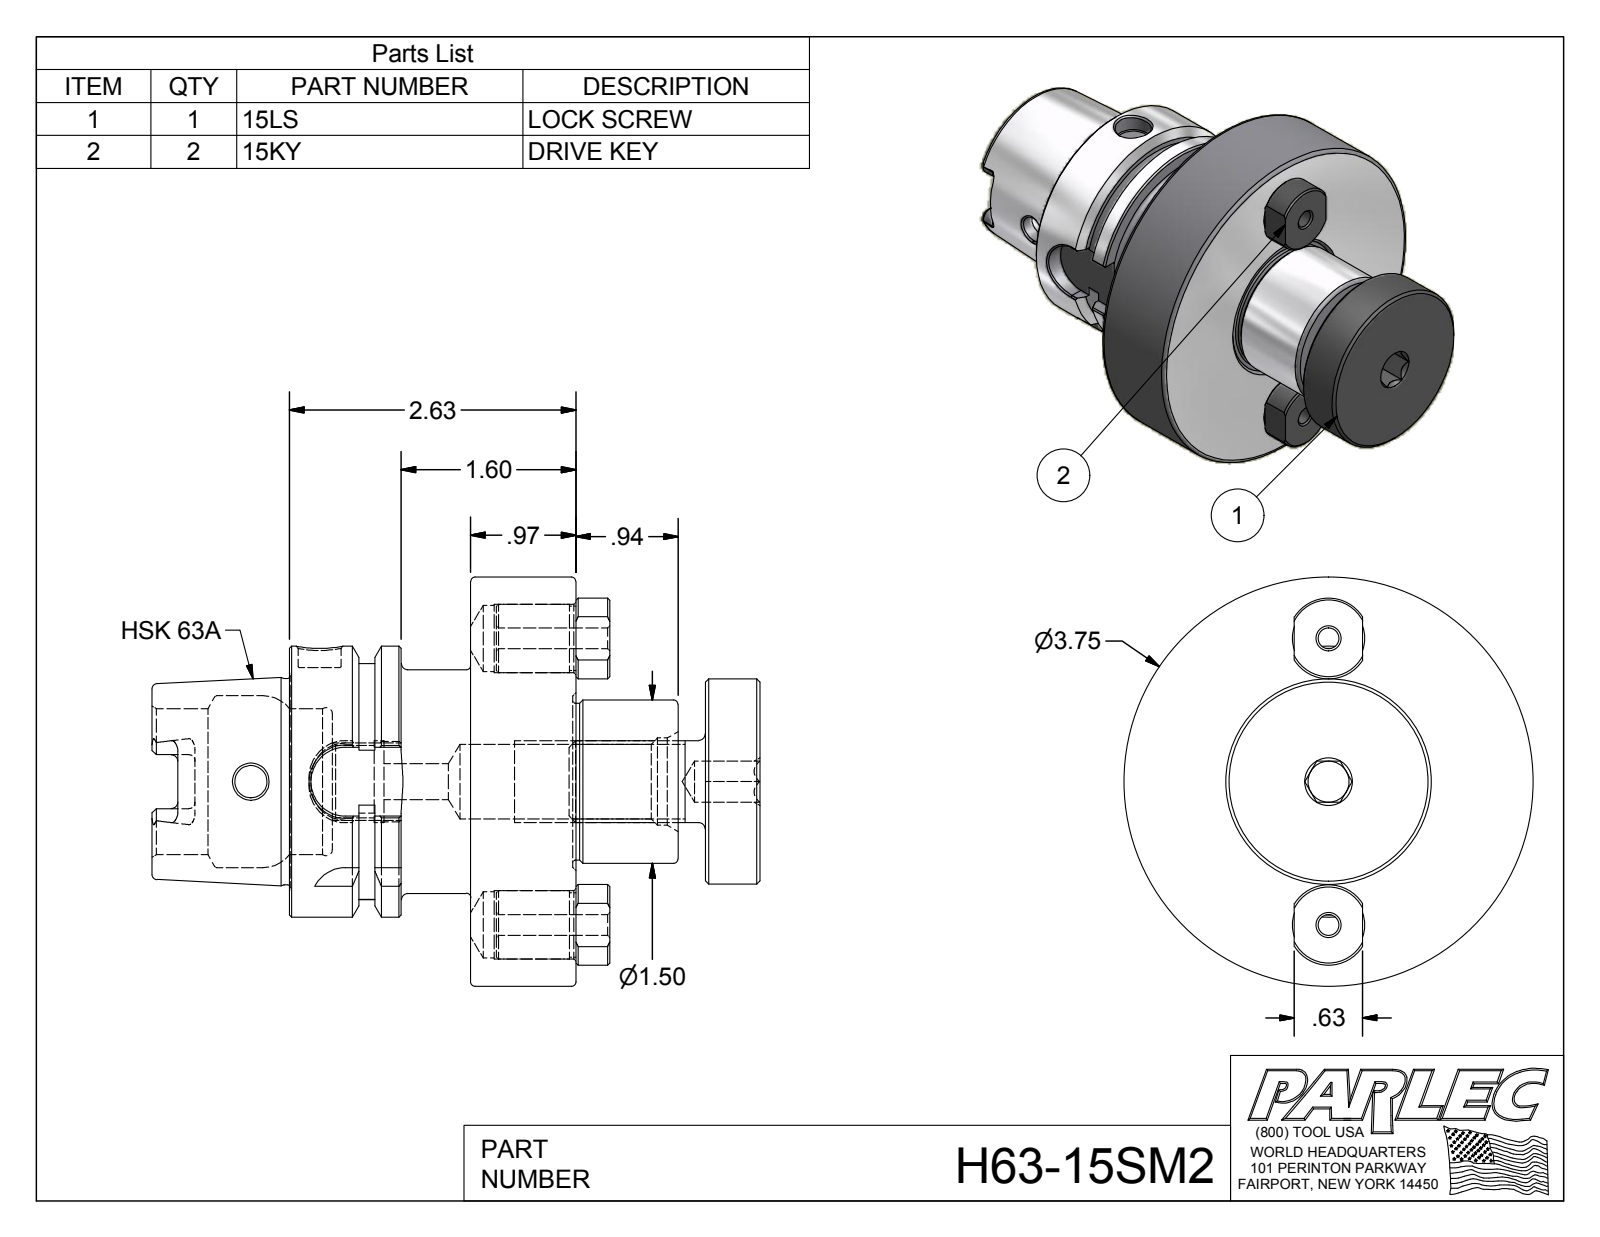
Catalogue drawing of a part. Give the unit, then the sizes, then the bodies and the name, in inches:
Units: inches
Overall size (bounding box): 5.572 × 3.75 × 3.75
Round holes (diameter × count): ⌀0.19 ×2, ⌀0.604 ×2, ⌀0.624 ×2, ⌀0.295 ×1, ⌀0.331 ×1, ⌀0.375 ×1, ⌀0.394 ×1, ⌀0.666 ×1, ⌀0.682 ×1, ⌀0.749 ×1, ⌀0.8 ×1, ⌀1.339 ×1
Round bosses / shafts (diameter × count): ⌀0.626 ×2, ⌀0.59 ×2, ⌀3.75 ×1, ⌀2.48 ×1, ⌀2.047 ×1, ⌀1.891 ×1, ⌀1.88 ×1, ⌀1.5 ×1
Partial cylindrical surfaces — rounded edges, fillets, slot ends (radius × count): R0.059 ×6, R0.113 ×4, R0.315 ×4, R0.37 ×2, R1.083 ×1
Main face-to-face distances: 0.965, 2.652, 1.687, 2.152, 1.187, 0.5, 1.66, 2.625, 3.812, 4.312
Hole centre spacings: 1.312, 2.624
Volume: 20.44 in³ · Surface area: 96.59 in²
Bodies: 4 solids, 218 faces (84 planar, 55 cylindrical, 79 other)
Part name (STEP PRODUCT): H63-15SM2; 15KY; 15LS
STEP written by: Autodesk Inventor 2012 (AUTOMOTIVE_DESIGN)
